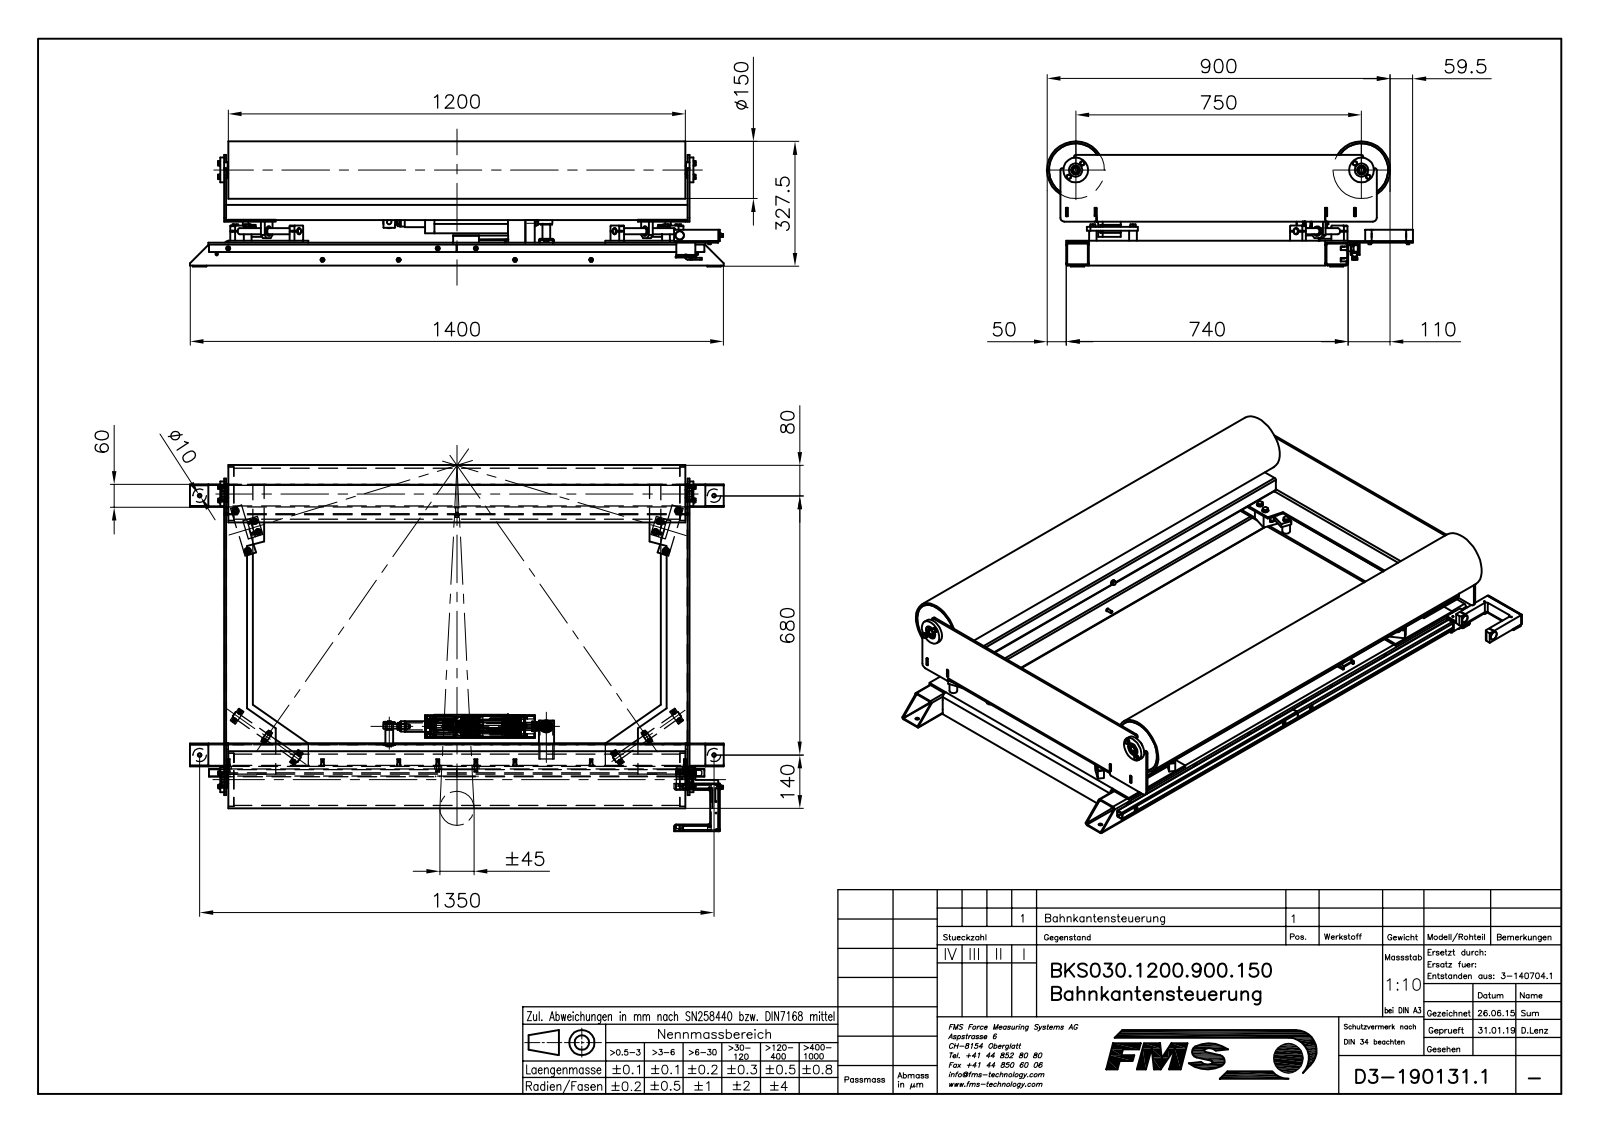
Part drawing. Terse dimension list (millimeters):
name: 071116.1_stp_01; 190131.1_stp_01; 31106632_01; 190131.1_stp
written by: SolidWorks 2023 (CONFIG_CONTROL_DESIGN)
unit: mm
bodies: 140 solids, 3549 faces (1632 planar, 1377 cylindrical, 540 other)
size: 1403 × 959.5 × 327.5
volume: 17 960 000 mm³; area: 6 748 000 mm²
holes: 34× ⌀5.15, 19× ⌀7, 12× ⌀2.6, 12× ⌀3.42, 12× ⌀4.3, 12× ⌀11, 10× ⌀10, 9× ⌀6.4, 8× ⌀3.4, 8× ⌀6.91, 8× ⌀9, 6× ⌀6
bosses: 14× ⌀9, 14× ⌀3, 10× ⌀6, 10× ⌀4, 8× ⌀20, 8× ⌀5.5, 7× ⌀2.15, 6× ⌀7
rounds: 41× R2, 29× R5, 22× R1, 17× R4, 14× R0.5, 10× R3, 10× R20, 8× R6
face distances: 3, 57, 5, 54, 62, 680, 37, 99, 119, 156
hole spacings: 24, 30, 1, 25, 32.88, 46.5, 47.1, 50.01
